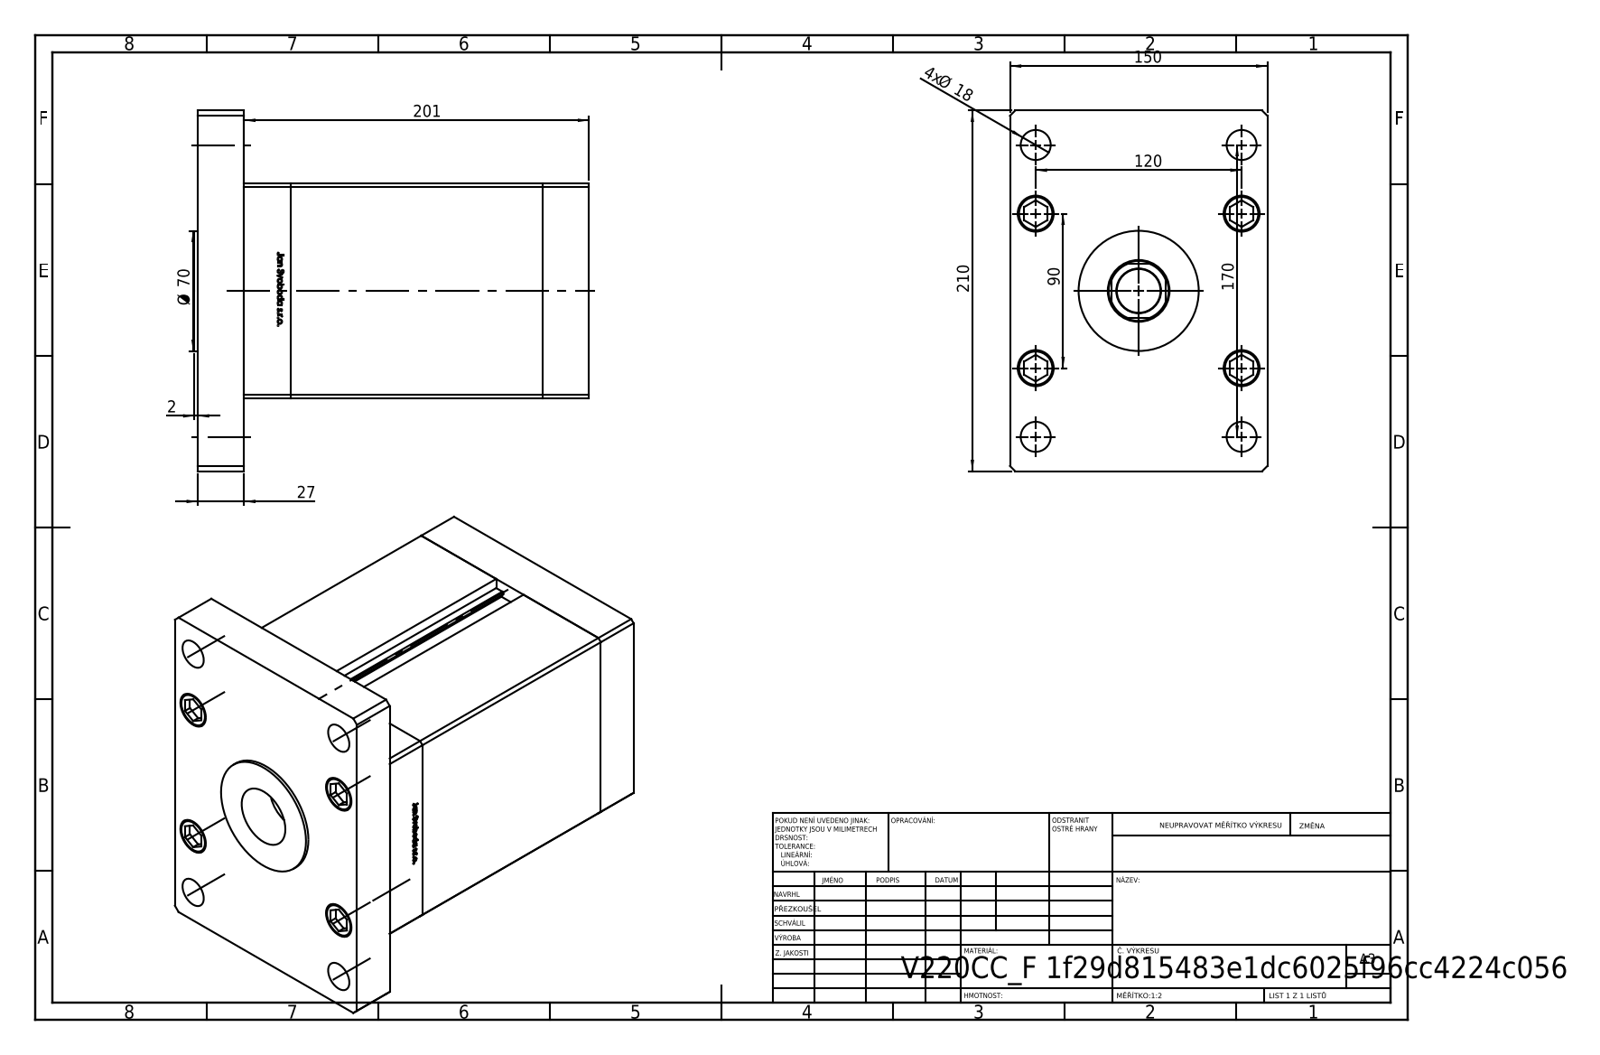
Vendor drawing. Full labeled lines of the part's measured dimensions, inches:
Part name (STEP PRODUCT): V220C BACK_F; V220C_F; ALLEN BOLT; V220C_F_MIDDLE (+2 more)
STEP written by: SolidWorks 2019 (CONFIG_CONTROL_DESIGN)
Units: inches
Bodies: 19 solids, 1298 faces (513 planar, 179 cylindrical, 606 other)
Overall size (bounding box): 9.055 × 8.268 × 5.906
Volume: 243.9 in³ · Surface area: 689.2 in²
Round holes (diameter × count): ⌀0.689 ×9, ⌀0.866 ×5, ⌀0.63 ×4, ⌀0.827 ×4, ⌀1.004 ×1, ⌀1.417 ×1, ⌀1.476 ×1
Round bosses / shafts (diameter × count): ⌀0.315 ×9, ⌀0.827 ×5, ⌀3.15 ×1, ⌀2.756 ×1
Partial cylindrical surfaces — rounded edges, fillets, slot ends (radius × count): R0.037 ×2, R0.689 ×1
Main face-to-face distances: 1.063, 6.85, 7.913, 5.906, 4.921, 5.787, 2.126, 8.976, 1.37, 0.307
Hole centre spacings: 2.008, 1.575, 2.953, 4.096, 4.724, 4.98, 5.118, 6.965
